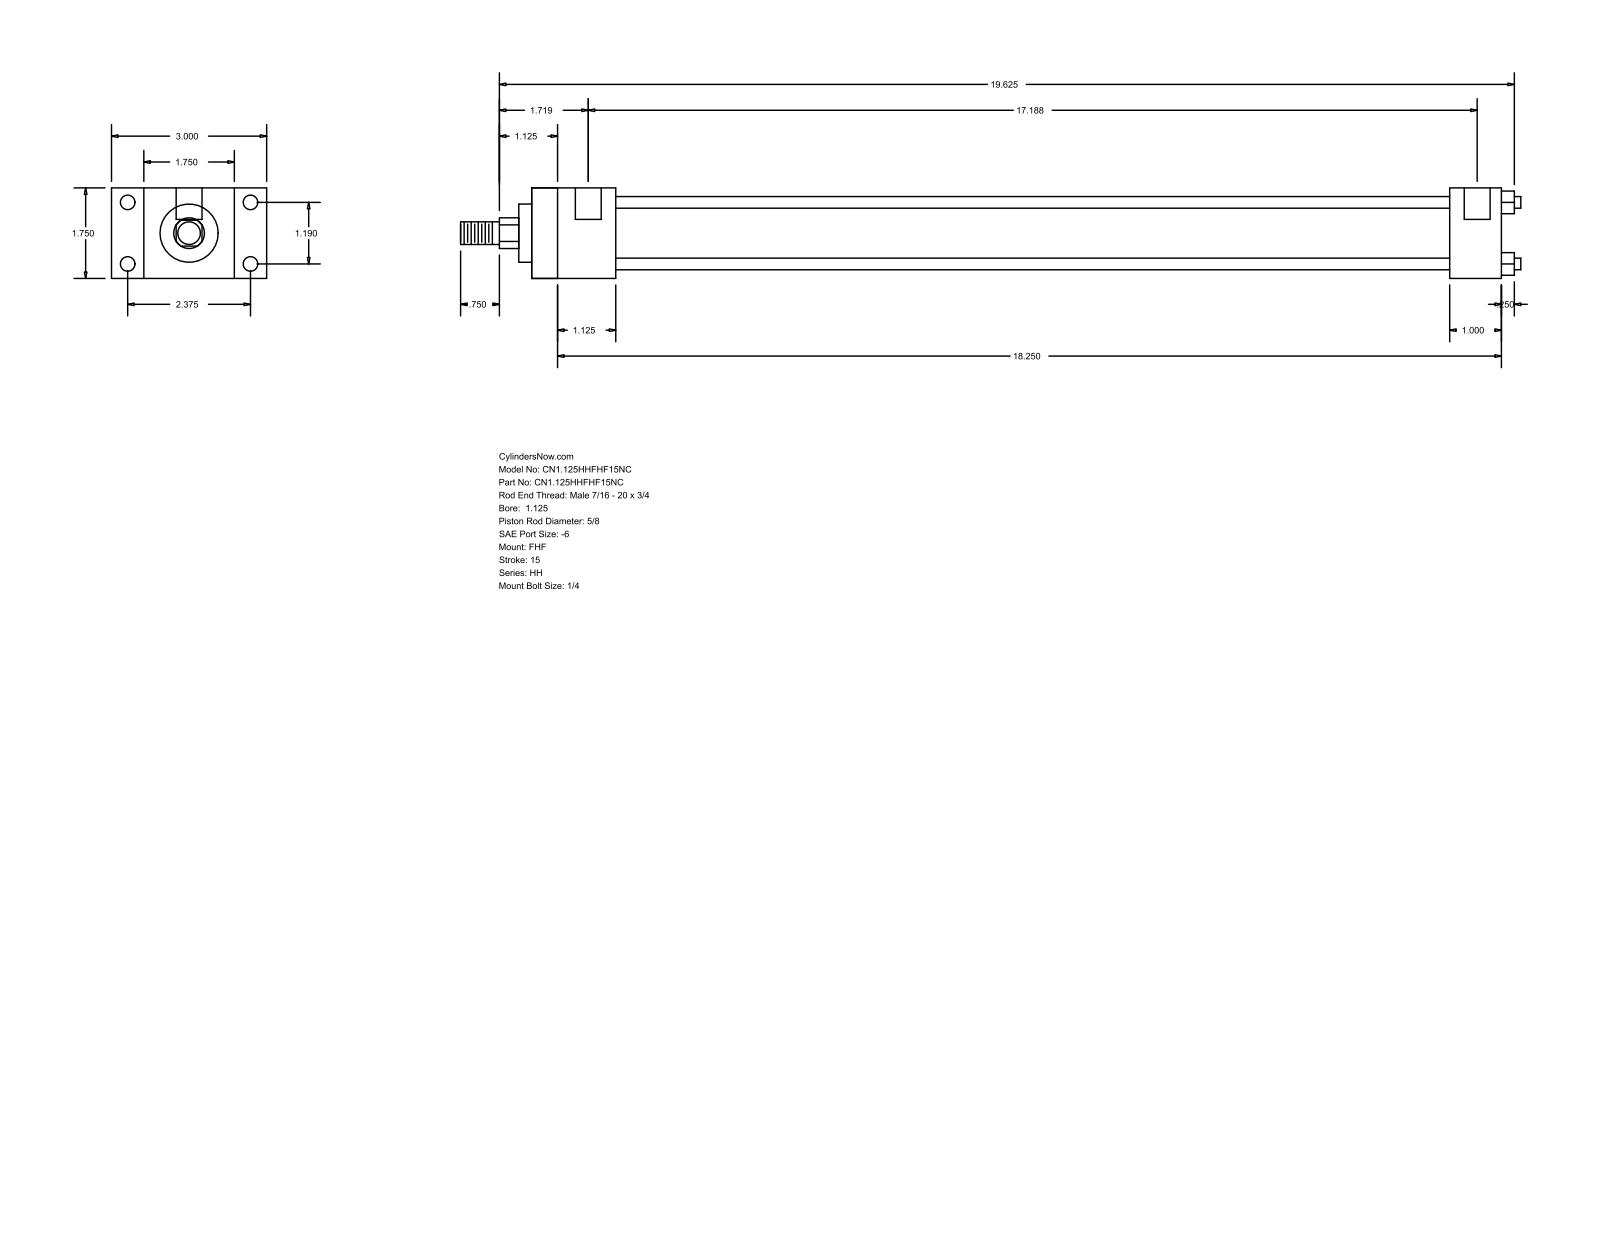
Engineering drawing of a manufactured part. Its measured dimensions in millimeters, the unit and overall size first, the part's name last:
Units: millimetres
Overall size (bounding box): 520.7 × 76.2 × 44.45
Round holes (diameter × count): ⌀5.56 ×4, ⌀7.14 ×4, ⌀12.7 ×2
Round bosses / shafts (diameter × count): ⌀5.71 ×4, ⌀34.92 ×1, ⌀28.57 ×1, ⌀15.88 ×1, ⌀11.11 ×1
Partial cylindrical surfaces — rounded edges, fillets, slot ends (radius × count): R7.54 ×1
Main face-to-face distances: 44.46, 15.87, 60.33, 41.27, 76.2, 476.24, 434.97, 450.85, 409.58, 25.39
Hole centre spacings: 30.22, 60.32, 67.47, 433.39, 3.17, 436.56
Bodies: 0 solids, 88 faces (60 planar, 28 cylindrical, 0 other)
Part name (STEP PRODUCT): HH_FHF__0112_0.625
STEP written by: GSSL Pune (CONFIG_CONTROL_DESIGN)
